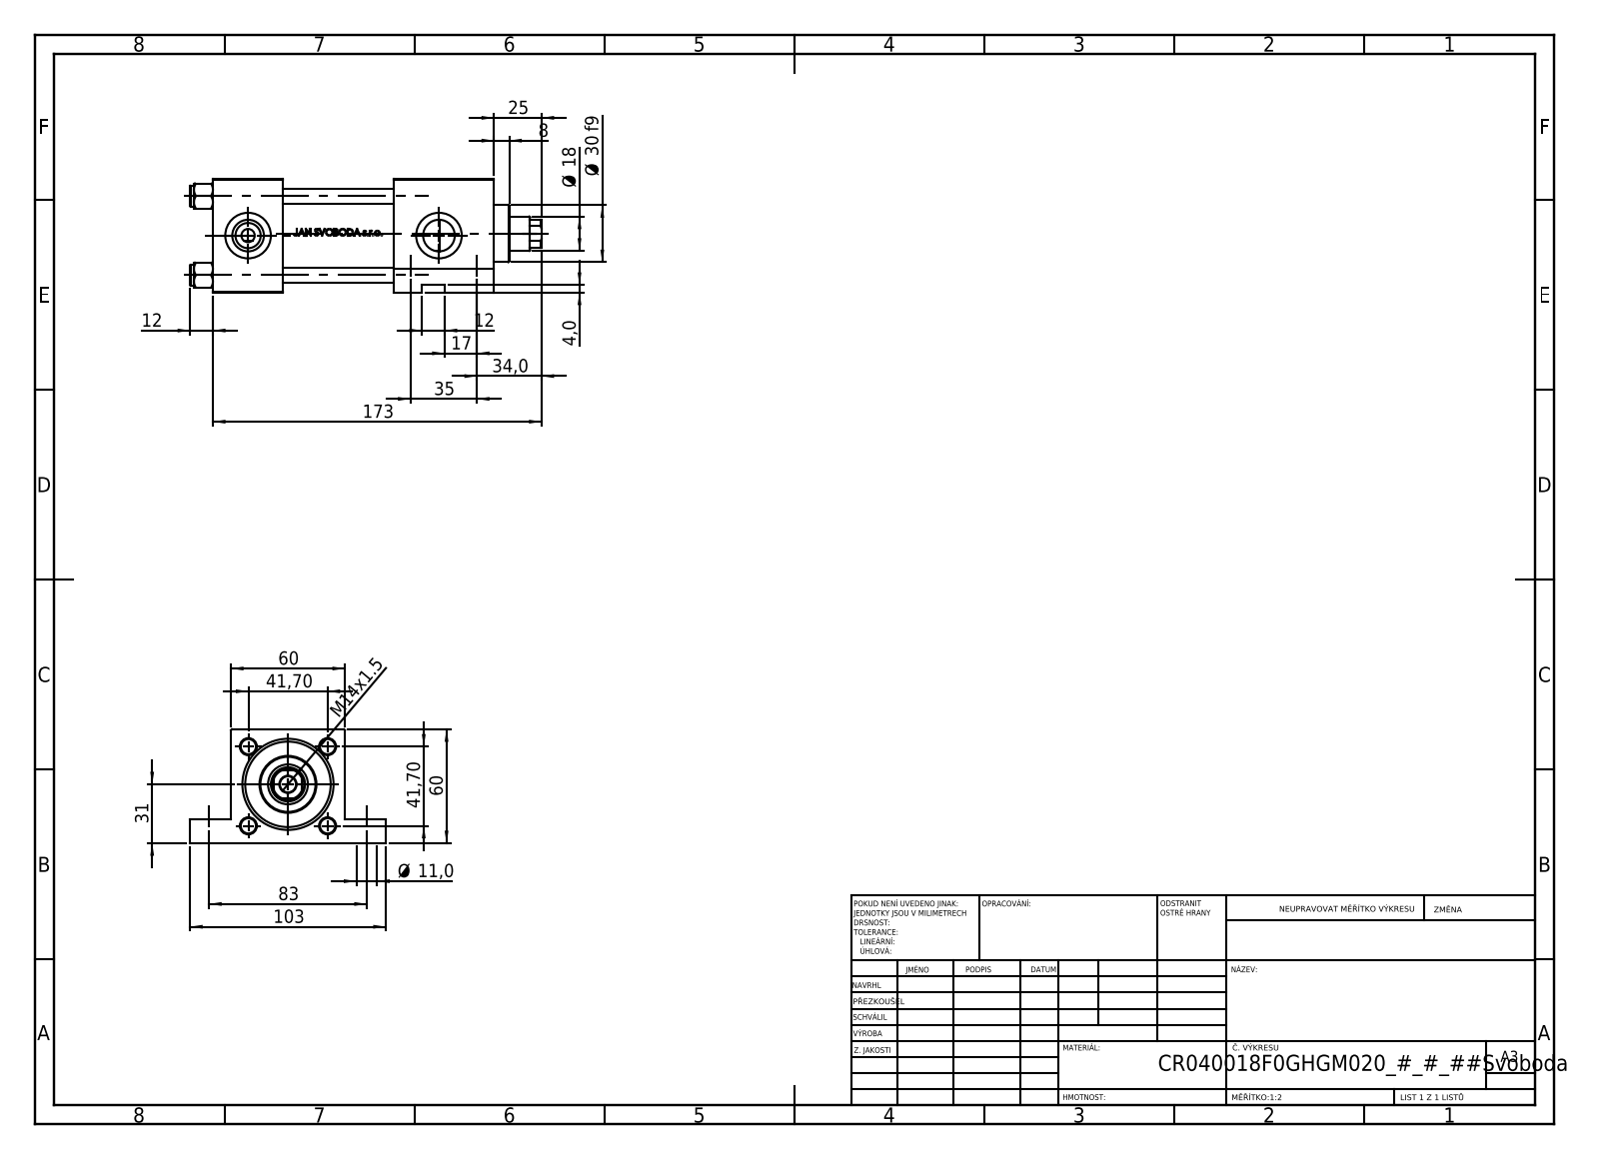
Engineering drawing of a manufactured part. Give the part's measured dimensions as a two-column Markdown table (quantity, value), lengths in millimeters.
| quantity | value |
| --- | --- |
| part name | V215CR_F_Body; V215_VC_A; NUT_M5_F; V215CR_F_TYCINKA (+1 more) |
| STEP written by | SolidWorks 2019 (CONFIG_CONTROL_DESIGN) |
| units | millimeters |
| bodies | 11 solids, 1118 faces (437 planar, 141 cylindrical, 540 other) |
| overall size | 185 × 103 × 60 |
| volume | 423 631 mm³ |
| surface area | 111 537 mm² |
| round holes (diameter × count) | 8 × 4, 7 × 2, 11 × 2, 11 × 2, 16.66 × 2, 24 × 2, 8.5 × 1, 18 × 1, 21 × 1, 31 × 1, 40 × 1, 45 × 1 |
| round bosses / shafts (diameter × count) | 11 × 4, 46 × 1, 30 × 1 |
| partial cylindrical surfaces (radius × count) | 8.5 × 1 |
| main face-to-face distances | 60, 37, 148, 111, 95, 58, 53, 119.3, 82.3, 24.3 |
| hole center spacings | 41.7, 28.79, 30.2, 35, 58.97, 83, 90.08, 100.5 |
